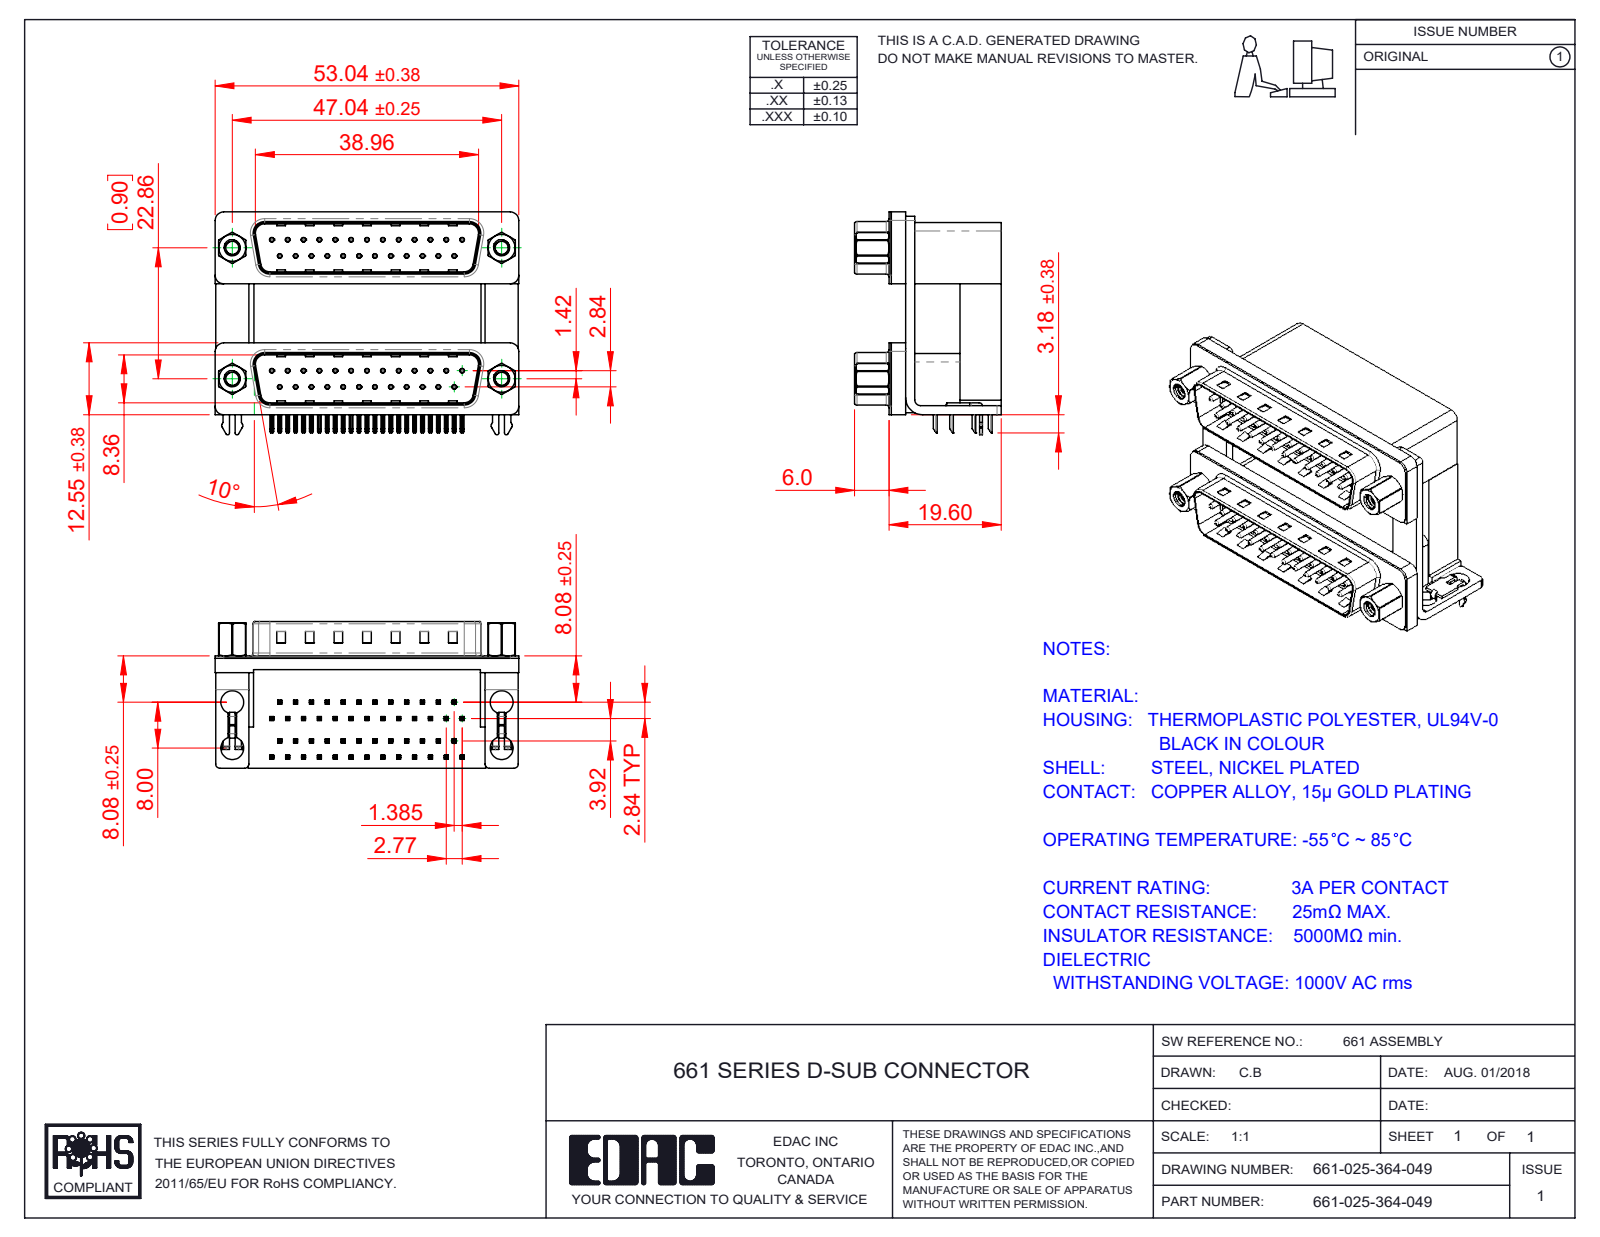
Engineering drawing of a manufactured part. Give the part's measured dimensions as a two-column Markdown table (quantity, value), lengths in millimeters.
| quantity | value |
| --- | --- |
| part name | 661 Contact Bottom Lower; 661 Mounting Bracket_ThruH; 661 Housing Lower_25 Contacts; 661 4 Prong Board Lock (+8 more) |
| STEP written by | SolidWorks 2020 (CONFIG_CONTROL_DESIGN) |
| units | millimeters |
| bodies | 69 solids, 5058 faces (3078 planar, 1490 cylindrical, 490 other) |
| overall size | 53.04 × 38.71 × 25.6 |
| volume | 22 858 mm³ |
| surface area | 24 497 mm² |
| round holes (diameter × count) | 0.35 × 50, 0.8 × 50, 2 × 4, 2.26 × 4, 2.29 × 4, 2.5 × 4, 3.2 × 4, 3.5 × 4, 4 × 4, 4.8 × 4, 5 × 4 |
| round bosses / shafts (diameter × count) | 0.75 × 50, 4.9 × 4, 4.75 × 4, 4 × 4, 3.9 × 4, 3.4 × 4, 3.3 × 4, 2.9 × 4 |
| partial cylindrical surfaces (radius × count) | 0.25 × 200, 0.12 × 100, 0.5 × 16, 1.5 × 14, 0.75 × 8, 0.9 × 8, 1.6 × 8, 2 × 8 |
| main face-to-face distances | 12, 22.86, 0.4, 19.2, 7.2, 10.7, 12.4, 16.7, 9.5, 2.5 |
| hole center spacings | 2.77, 3.16, 5.54, 8.31, 11.08, 13.85, 16.62, 5.03 |
